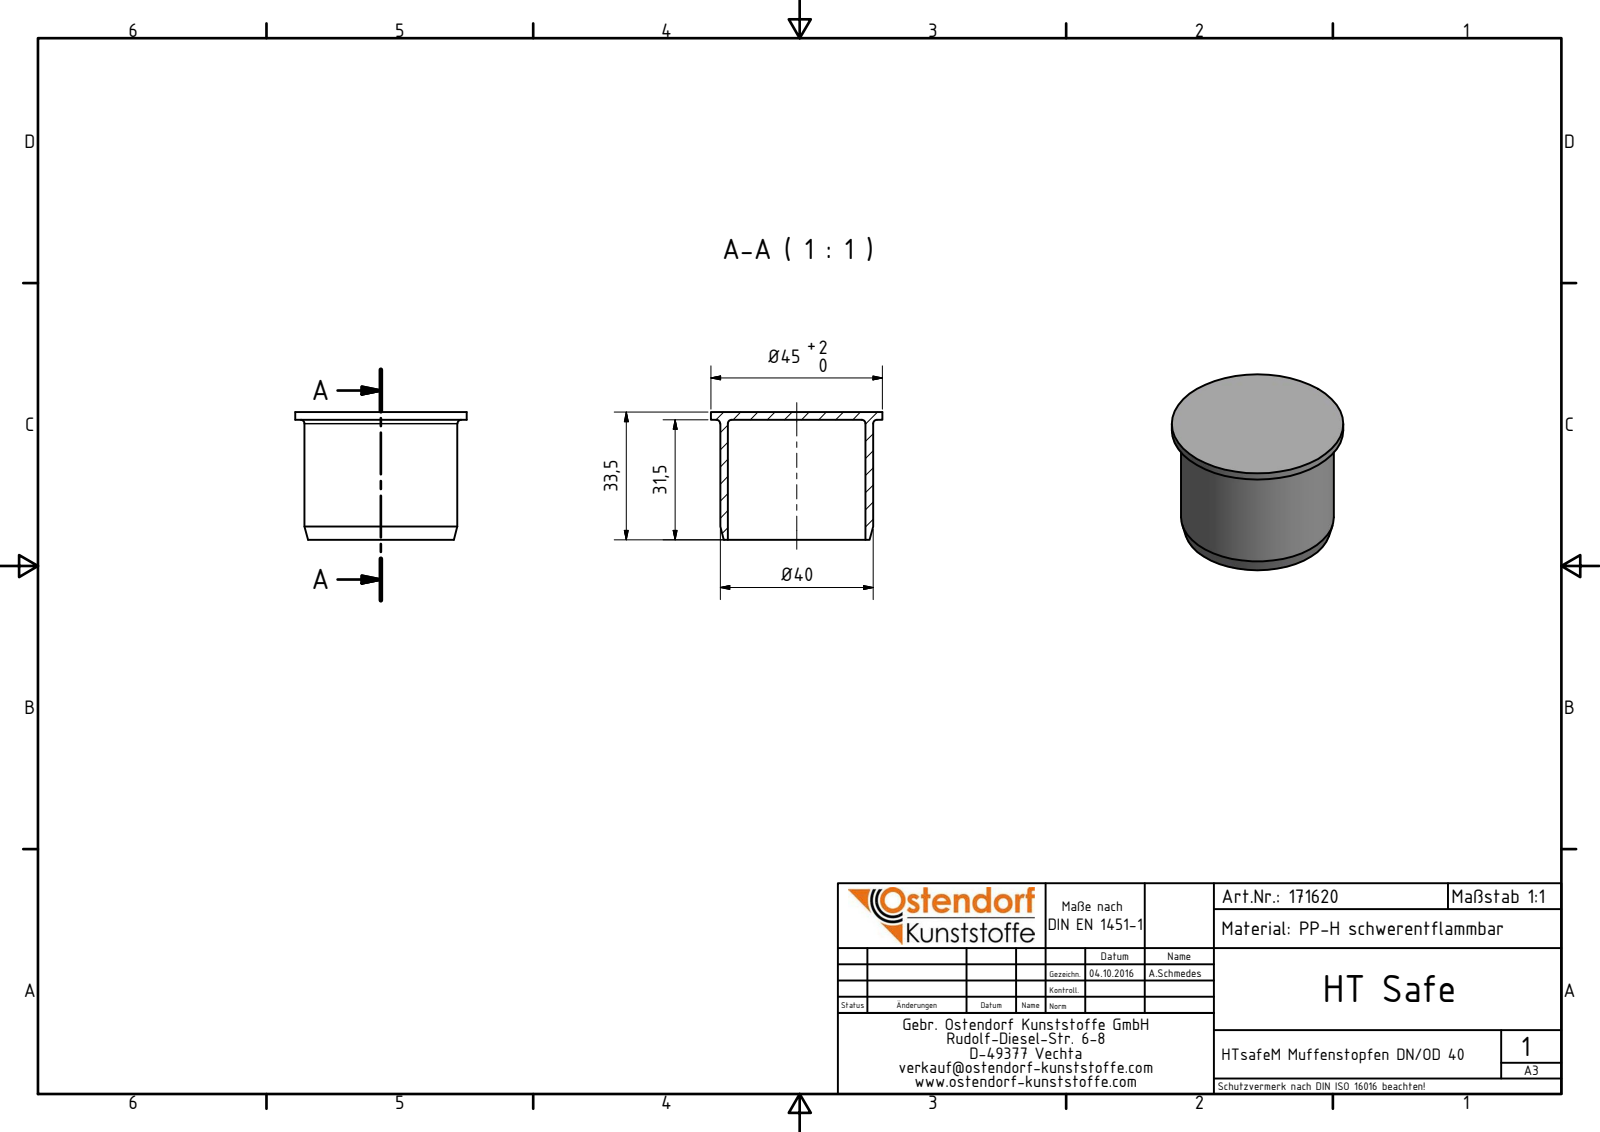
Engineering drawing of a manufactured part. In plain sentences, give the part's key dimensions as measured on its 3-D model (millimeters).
The part is named "171620 HTsafeM DN_OD 40". Its 3-D file was written by "Autodesk Inventor 2016 (AUTOMOTIVE_DESIGN)". It is 1 solid with 10 faces: 4 planar, 3 cylindrical and 3 other. Overall it measures 45 by 45 by 33.5 millimeters. Its volume is 10 579 cubic millimeters and its surface area 10 801 square millimeters. Round holes: 1 of diameter 36.15. Round bosses or shafts: 1 of diameter 45, 1 of diameter 40.15. The main face-to-face distances are 2, 31.5, 33.5.
